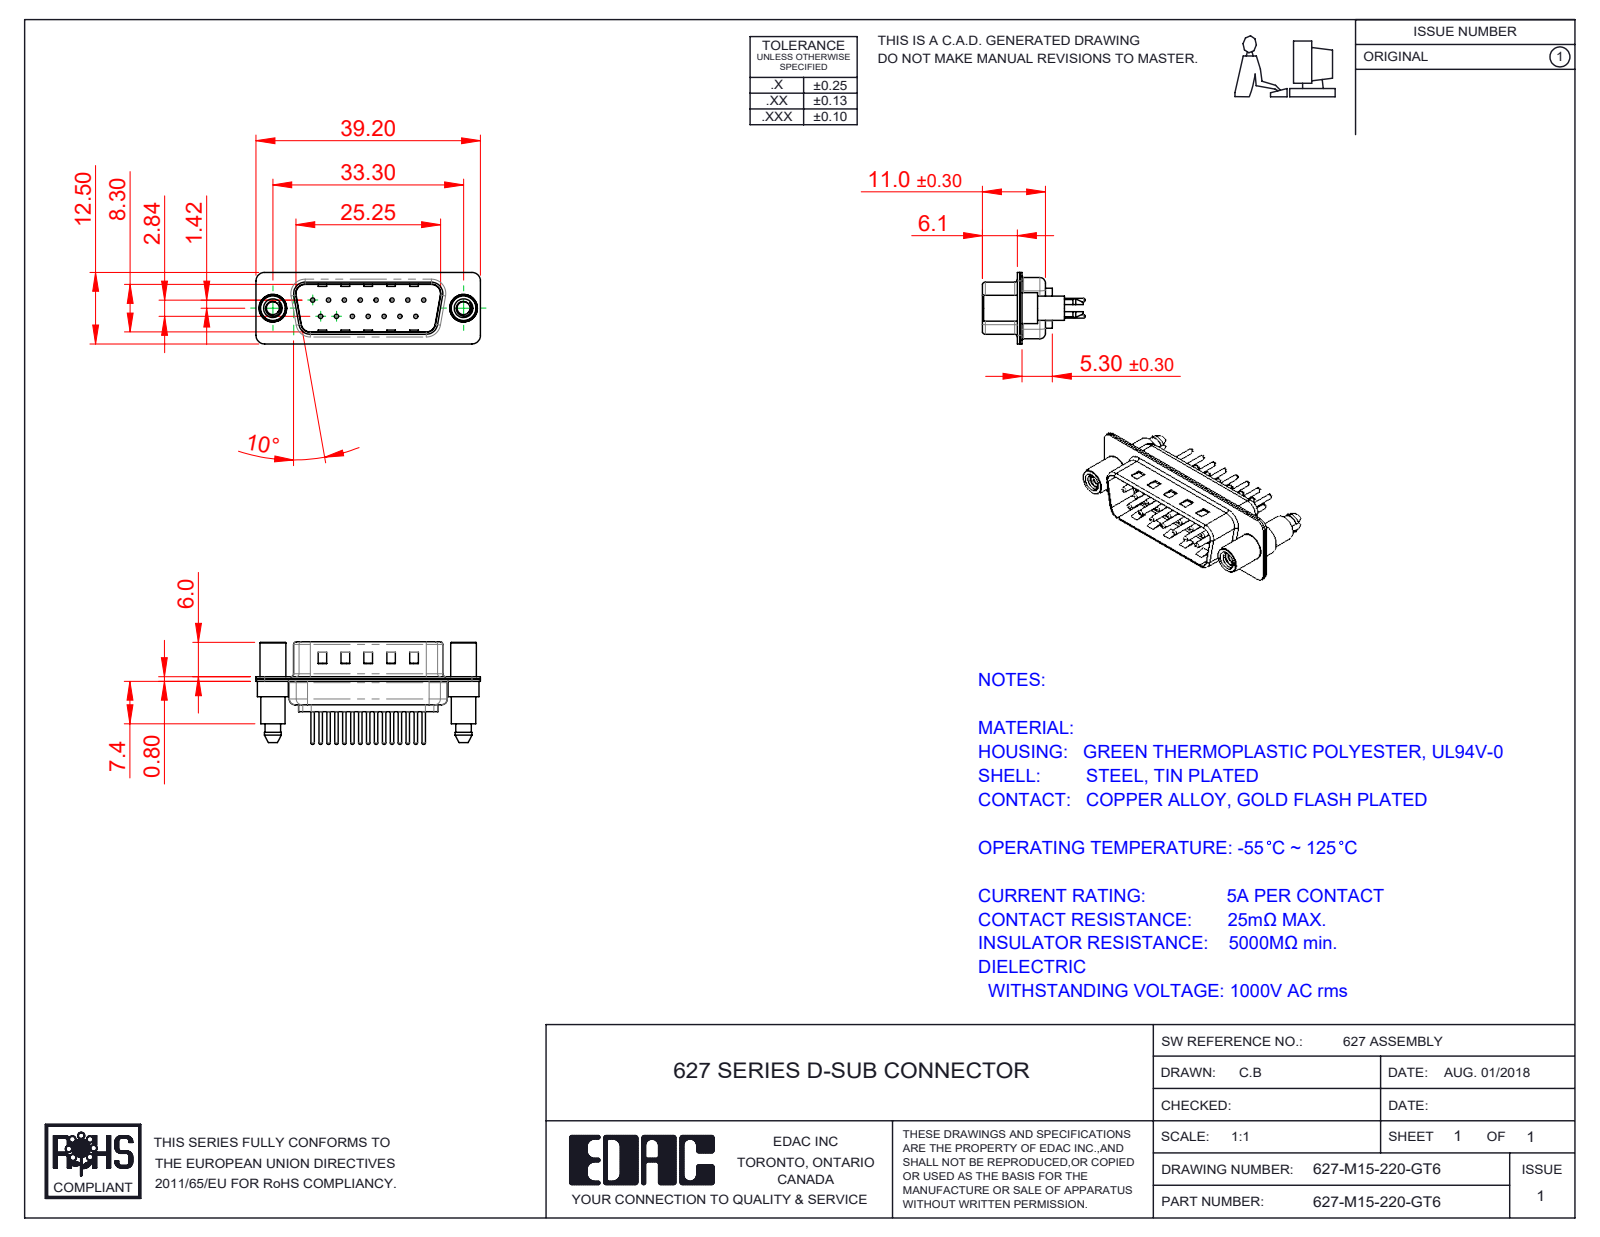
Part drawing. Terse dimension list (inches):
name: 627M Shell Front_15 Contacts; 627M 4-40 Threaded Standoff and Boardlock; 627M Shell Rear_15 Contacts; 627M Contact Row 1_20 (+3 more)
written by: SolidWorks 2020 (CONFIG_CONTROL_DESIGN)
unit: in
bodies: 20 solids, 947 faces (262 planar, 371 cylindrical, 314 other)
size: 1.543 × 0.705 × 0.492
volume: 0.133 in³; area: 8.178 in²
holes: 15× ⌀0.03, 15× ⌀0.063, 15× ⌀0.079, 2× ⌀0.089, 2× ⌀0.157, 2× ⌀0.189
bosses: 15× ⌀0.059, 15× ⌀0.024, 2× ⌀0.213, 2× ⌀0.193, 2× ⌀0.177, 2× ⌀0.167
rounds: 18× R0.059, 12× R0.079, 10× R0.063, 8× R0.02, 4× R0.01, 4× R0.024, 4× R0.026, 4× R0.035
face distances: 0.016, 0.031, 0.374, 0.358, 0.343, 0.39, 0.209, 0.047, 0.24, 0.224
hole spacings: 0.124, 0.109, 0.218, 0.327, 0.436, 0.198, 0.198, 0.294
